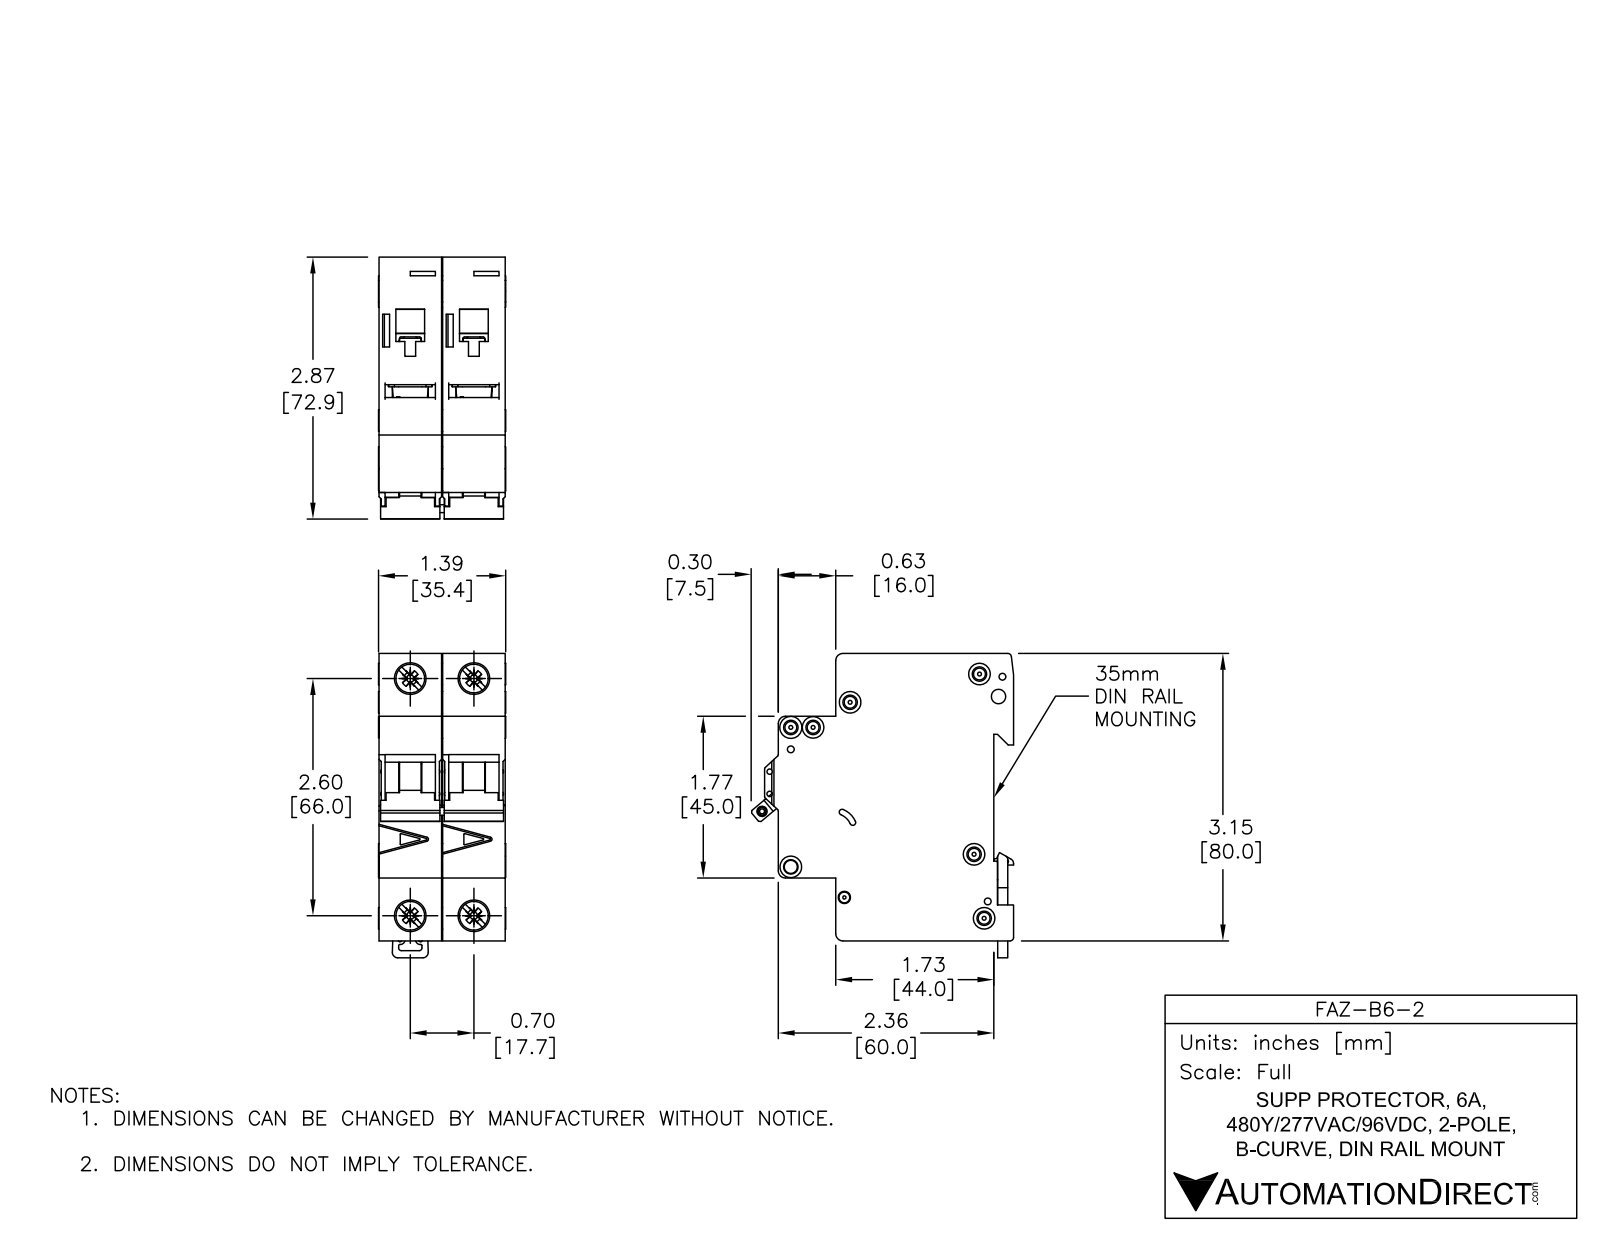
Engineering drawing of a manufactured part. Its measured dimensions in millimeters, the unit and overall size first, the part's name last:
Units: millimetres
Overall size (bounding box): 84.78 × 73.04 × 35.4
Round holes (diameter × count): ⌀3.6 ×6, ⌀1.9 ×3, ⌀1.09 ×2, ⌀1.5 ×2, ⌀4 ×2, ⌀7.15 ×2, ⌀8.2 ×2, ⌀2.15 ×1, ⌀2.2 ×1, ⌀2.55 ×1, ⌀3.3 ×1, ⌀3.4 ×1
Round bosses / shafts (diameter × count): ⌀6 ×4, ⌀8.2 ×2, ⌀2.5 ×2
Partial cylindrical surfaces — rounded edges, fillets, slot ends (radius × count): R0.25 ×49, R0.5 ×19, R2 ×10, R0.2 ×8, R1 ×8, R0.8 ×2, R1.8 ×2, R3 ×2
Main face-to-face distances: 17.7, 17.5, 35.2, 79.48, 5.5, 49.5, 44, 65.5, 60, 16
Hole centre spacings: 6.2, 13.64, 17.7, 66, 68.33, 4.81, 5.19, 5.61
Volume: 149 808 mm³ · Surface area: 38 799 mm²
Bodies: 8 solids, 1104 faces (466 planar, 396 cylindrical, 242 other)
Part name (STEP PRODUCT): FAZ-B6-2
STEP written by: SolidWorks 2014 (AUTOMOTIVE_DESIGN)
